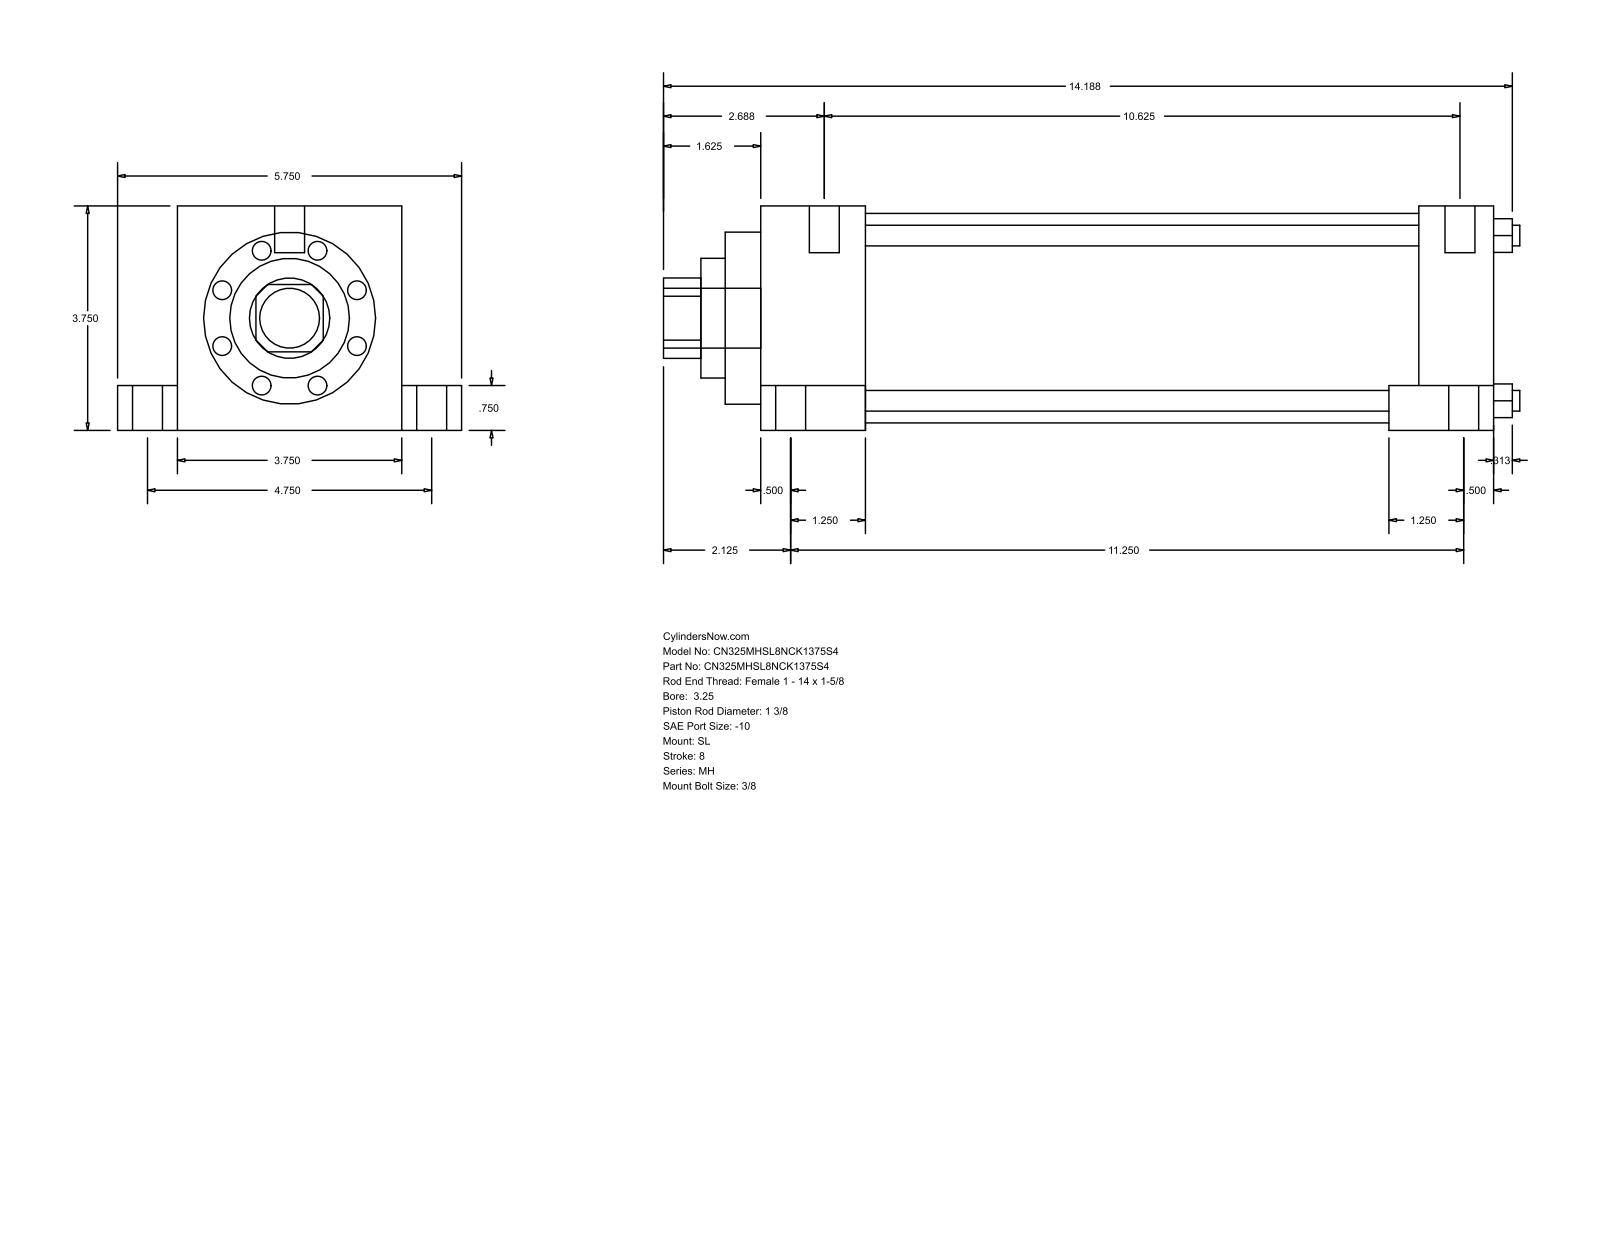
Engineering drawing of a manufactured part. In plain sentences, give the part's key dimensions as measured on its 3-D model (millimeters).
The part is named "MH_SL__0325_1.375". Its 3-D file was written by "GSSL Pune (CONFIG_CONTROL_DESIGN)". It is 0 solids with 110 faces: 77 planar, 33 cylindrical and 0 other. Overall it measures 363.54 by 146.05 by 95.25 millimeters. Round holes: 4 of diameter 8.76, 1 of diameter 34.92, 1 of diameter 50.8, 1 of diameter 73.03, 1 of diameter 88.9. Round bosses or shafts: 6 of diameter 12.7, 4 of diameter 19.05, 4 of diameter 5.56, 1 of diameter 25.4. Partial cylindrical surfaces (rounded edges, fillets, slot ends): 1 of radius 17.06. The main face-to-face distances are 95.24, 311.16, 44.45, 266.71, 25.41, 120.65, 19.05, 76.19, 279.41, 234.96. The hole center spacings are 49.57, 70.1, 99.14.
